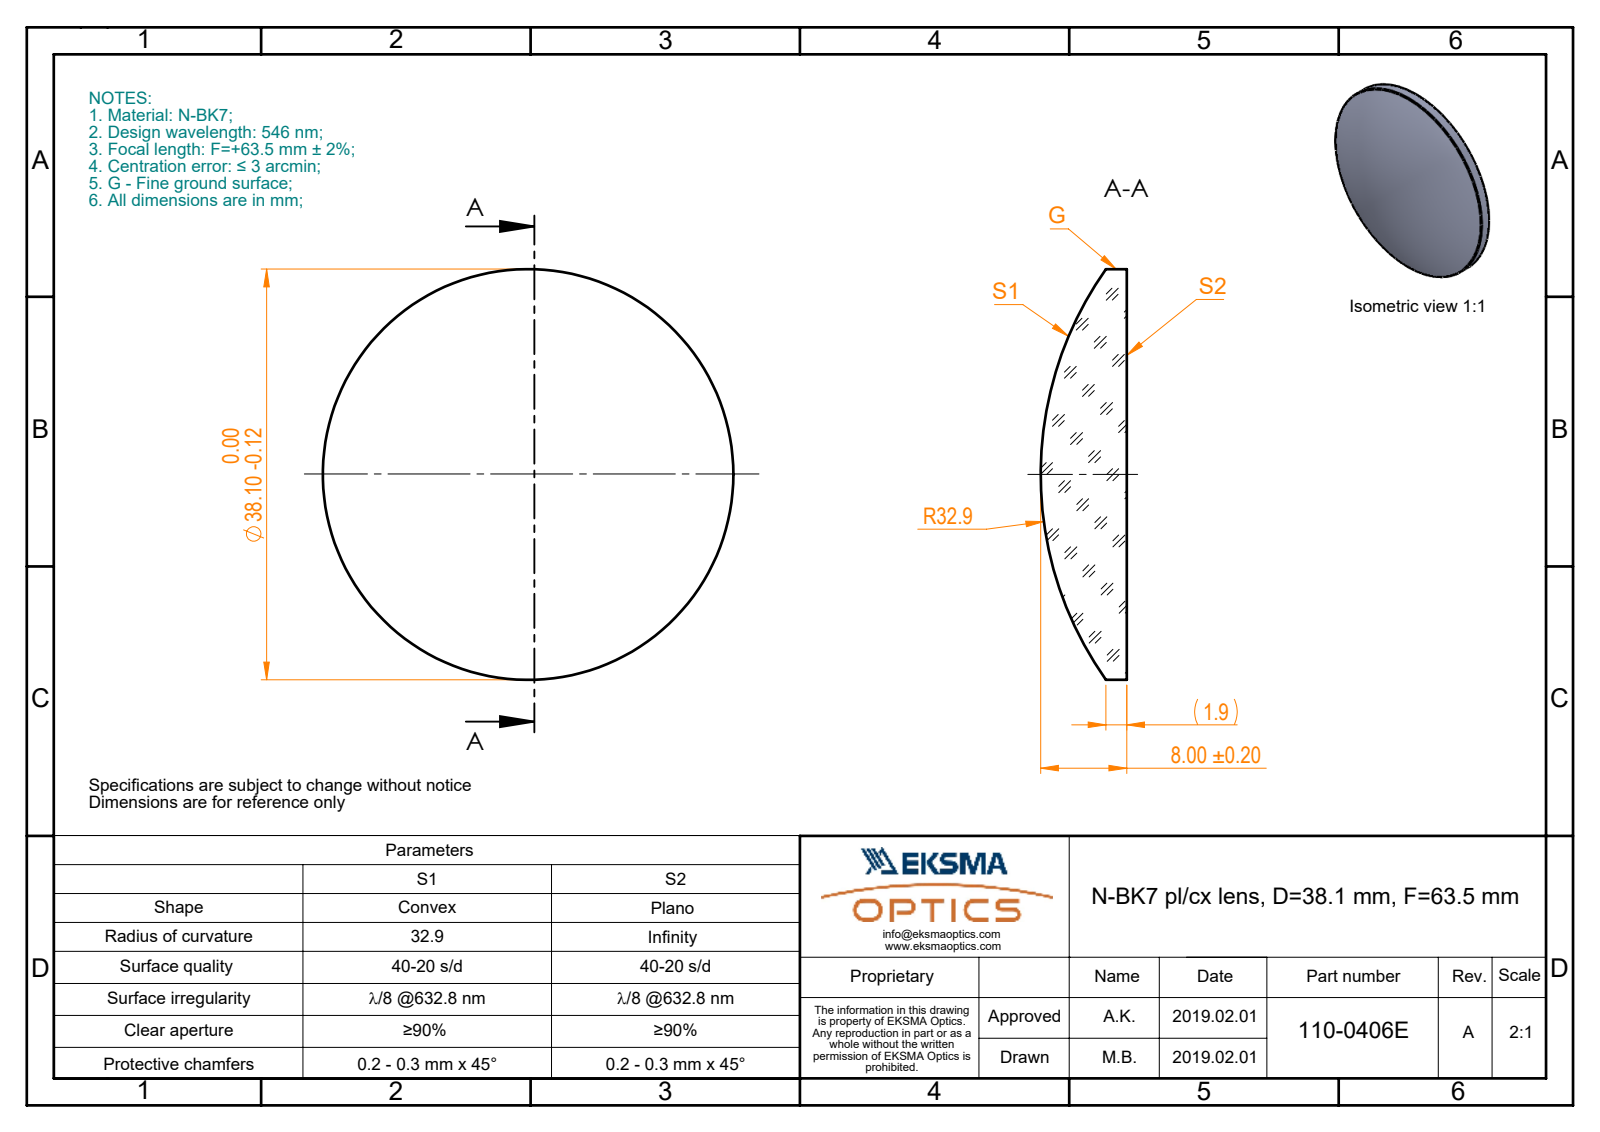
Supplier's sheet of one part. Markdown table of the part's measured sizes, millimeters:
| quantity | value |
| --- | --- |
| part name | 110-0406E BK7 pl-cx 38.1 F63.5 |
| STEP written by | SolidWorks 2017 (CONFIG_CONTROL_DESIGN) |
| units | millimeters |
| bodies | 1 solid, 5 faces (1 planar, 2 cylindrical, 2 other) |
| overall size | 38.1 × 38.1 × 8 |
| volume | 5 779 mm³ |
| surface area | 2 627 mm² |
| round bosses / shafts (diameter × count) | 38.1 × 1 |
